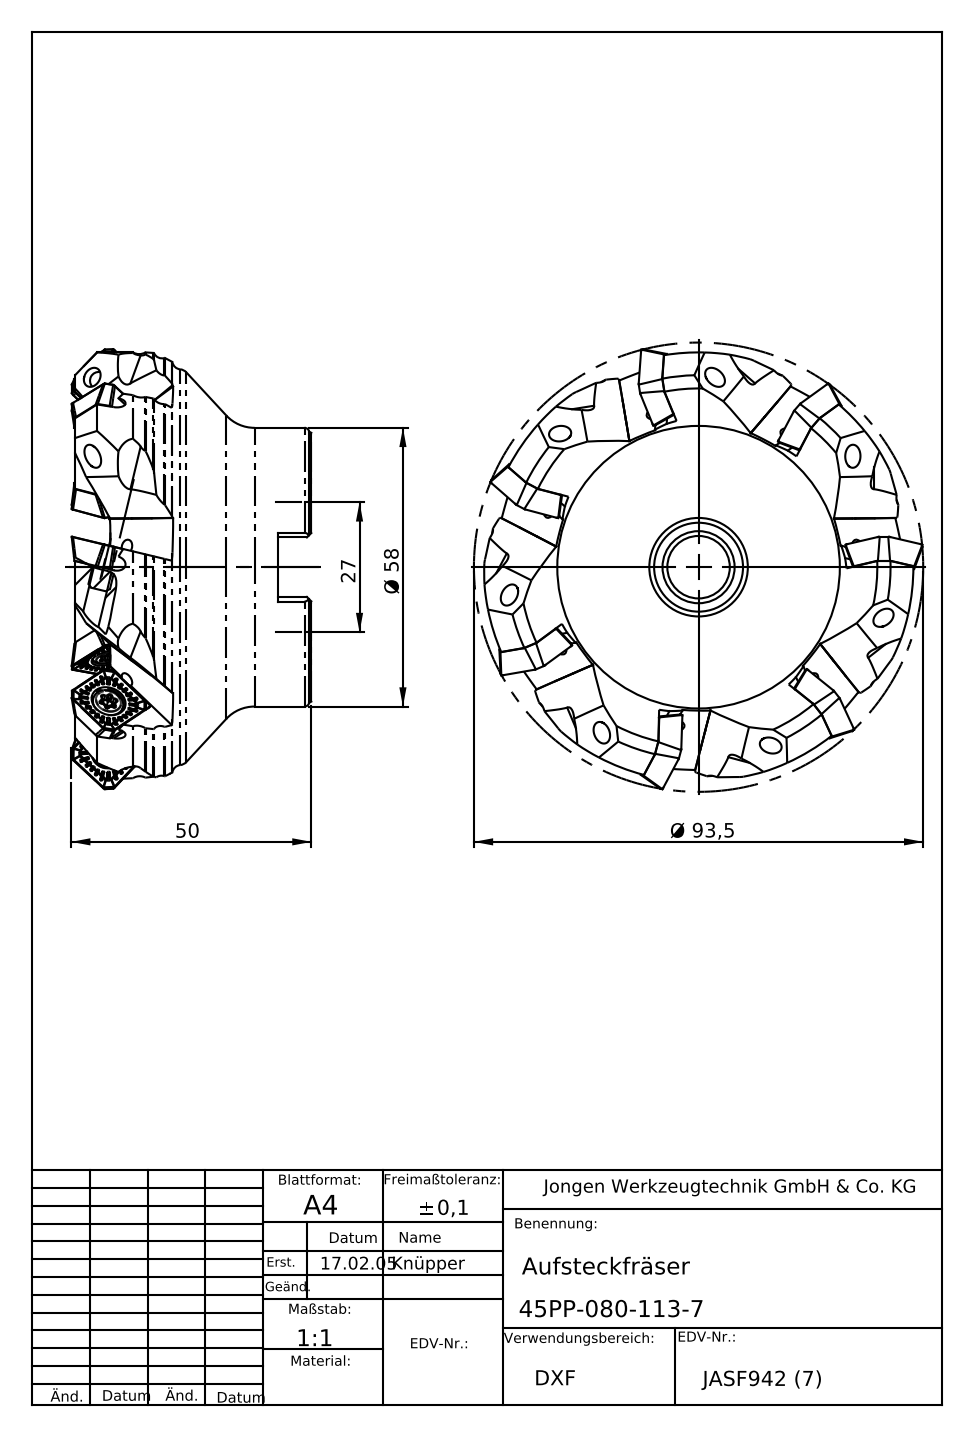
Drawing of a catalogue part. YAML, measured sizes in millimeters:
part_name: "45PP-080-113-7"
step_written_by: "SolidWorks 2013 (AUTOMOTIVE_DESIGN)"
units: millimeters
bodies: {solids: 1, faces: 230, planar: 93, cylindrical: 34, other: 103}
overall_size: [93.45, 93.45, 50.08]
volume: 171936
surface_area: 27707
round_holes:
  - {diameter: 3, count: 7}
  - {diameter: 13, count: 1}
  - {diameter: 18.5, count: 1}
  - {diameter: 27, count: 1}
  - {diameter: 27.15, count: 1}
  - {diameter: 27.3, count: 1}
round_bosses_or_shafts:
  - {diameter: 58, count: 1}
partial_cylinders:
  - {radius: 1.5, count: 7}
  - {radius: 2.55, count: 7}
  - {radius: 44.7, count: 1}
face_to_face_distances: [41.4, 6.95, 34.45, 24, 17.05, 17.4, 12.4, 29.4, 22.45, 5.4]
